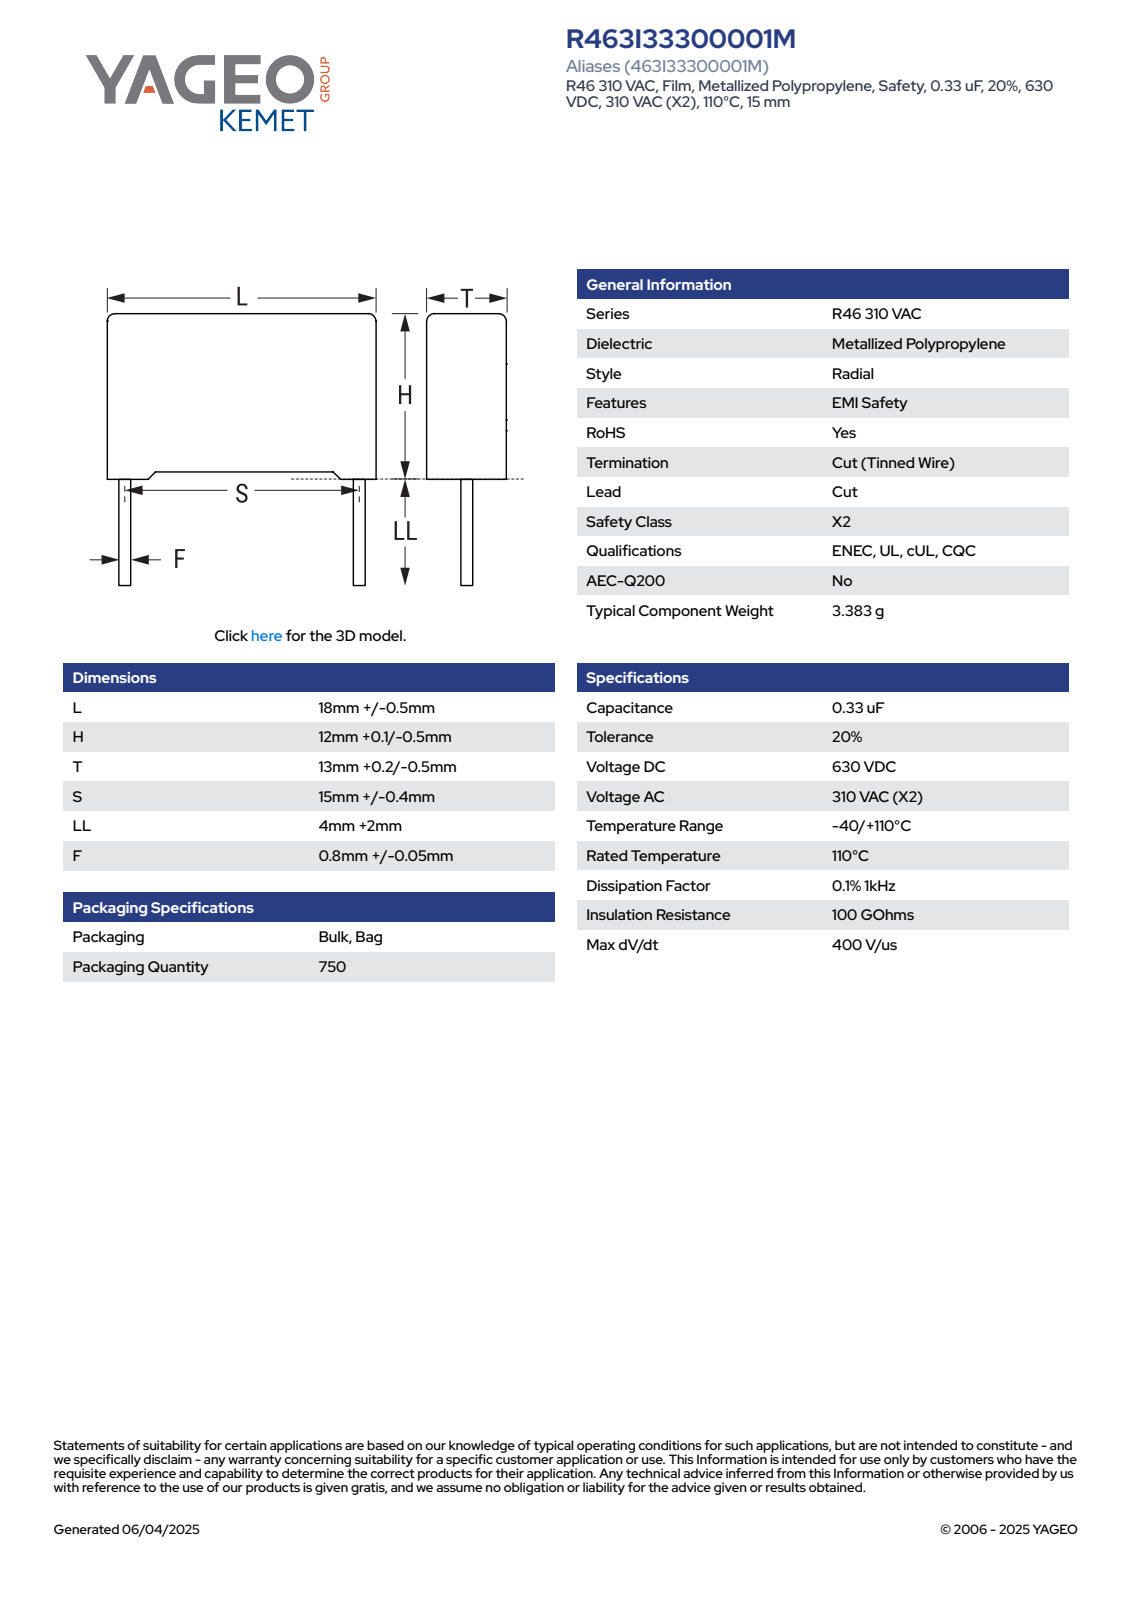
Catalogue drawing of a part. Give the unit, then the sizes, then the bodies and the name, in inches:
Units: inches
Overall size (bounding box): 0.728 × 0.713 × 0.52
Round bosses / shafts (diameter × count): ⌀0.033 ×2
Partial cylindrical surfaces — rounded edges, fillets, slot ends (radius × count): R0.02 ×4
Main face-to-face distances: 0.52, 0.447, 0.728, 0.024, 0.03, 0.476, 0.704, 0.495, 0.017, 0.013
Volume: 0.171 in³ · Surface area: 2.06 in²
Bodies: 4 solids, 85 faces (77 planar, 8 cylindrical, 0 other)
Part name (STEP PRODUCT): CFR_RB2_18X12X13_L18.5H12.1T13.2S15LL6F0.85
STEP written by: SolidWorks 2021 (AUTOMOTIVE_DESIGN)
